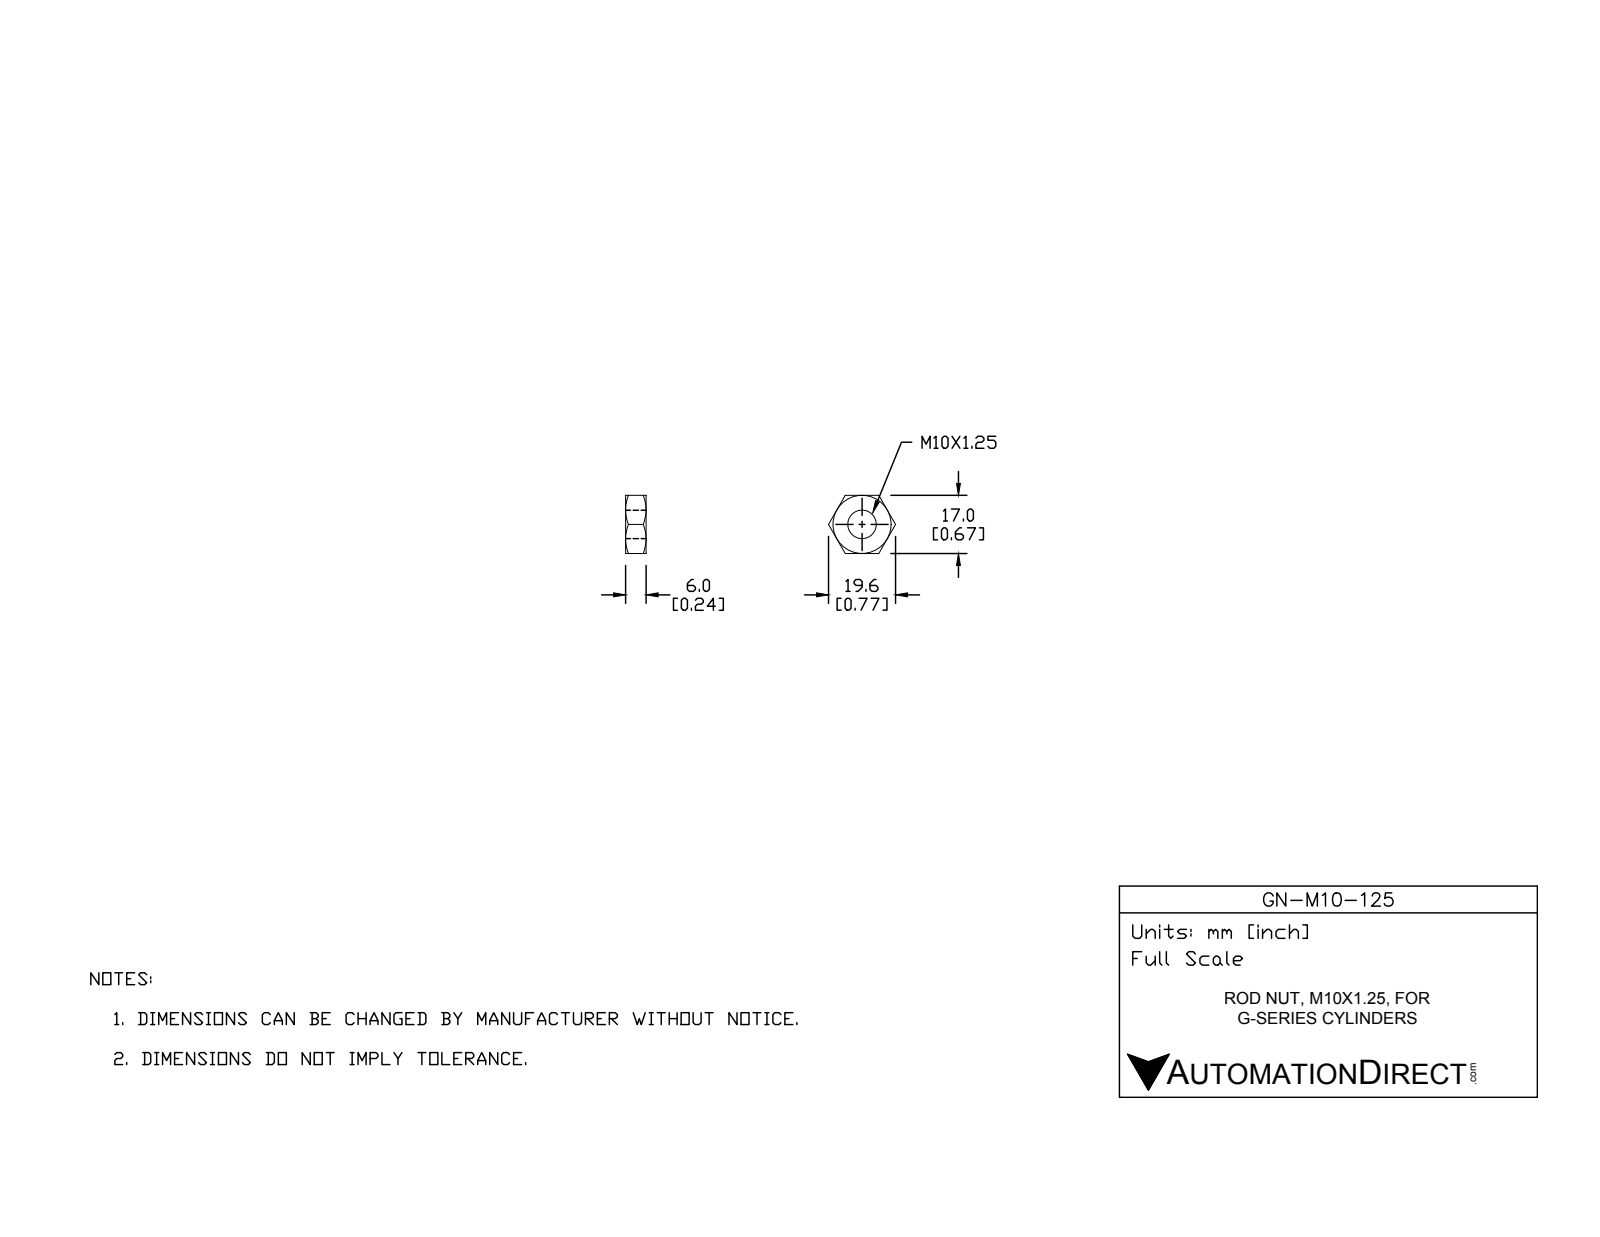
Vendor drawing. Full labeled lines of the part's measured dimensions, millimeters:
Part name (STEP PRODUCT): GN-M10-125
STEP written by: SolidWorks 2017 (AUTOMOTIVE_DESIGN)
Units: millimetres
Bodies: 1 solid, 24 faces (8 planar, 2 cylindrical, 14 other)
Overall size (bounding box): 19.63 × 17 × 6
Volume: 1 118 mm³ · Surface area: 864 mm²
Round holes (diameter × count): ⌀8.8 ×1
Main face-to-face distances: 6, 17
